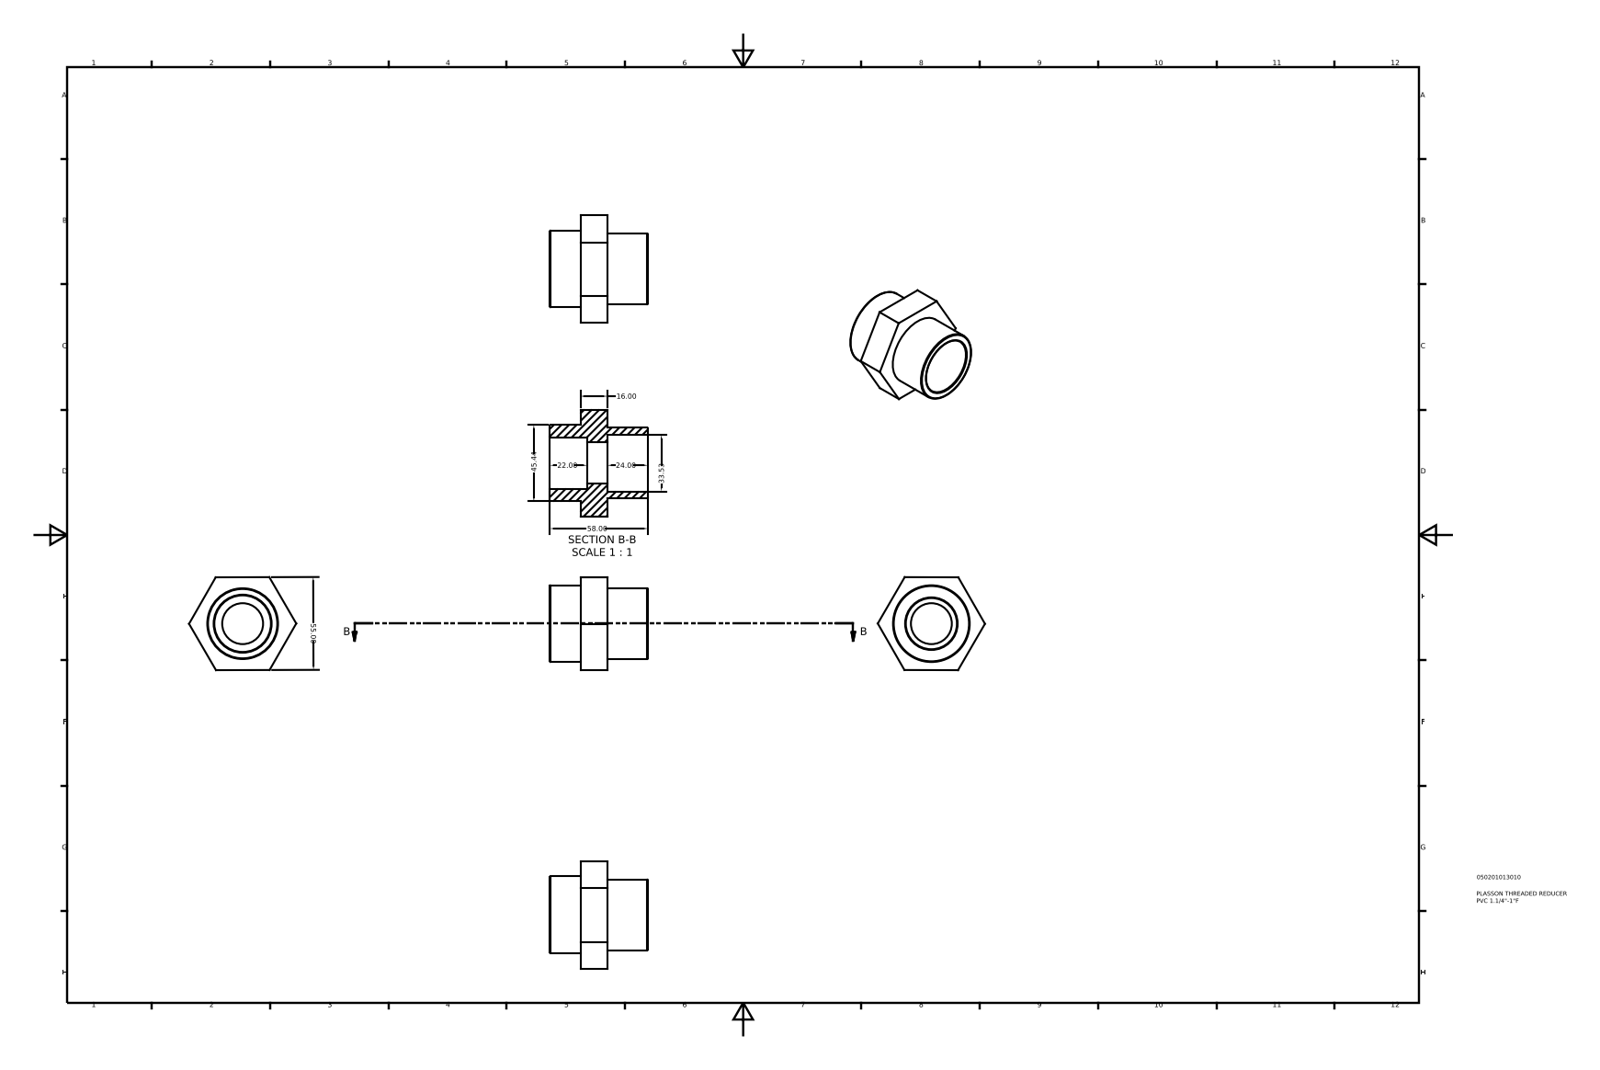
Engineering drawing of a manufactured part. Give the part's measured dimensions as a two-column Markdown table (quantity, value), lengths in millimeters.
| quantity | value |
| --- | --- |
| part name | 050201013010 |
| STEP written by | Autodesk Inventor 2015 (AUTOMOTIVE_DESIGN) |
| units | millimeters |
| bodies | 1 solid, 21 faces (12 planar, 5 cylindrical, 4 other) |
| overall size | 63.51 × 58 × 55.09 |
| volume | 61 614 mm³ |
| surface area | 18 544 mm² |
| round holes (diameter × count) | 24.23 × 1, 30.29 × 1, 33.53 × 1 |
| round bosses / shafts (diameter × count) | 45.44 × 1, 41.91 × 1 |
| main face-to-face distances | 55.04, 16, 18, 34, 55, 58, 40, 24, 22, 4 |
